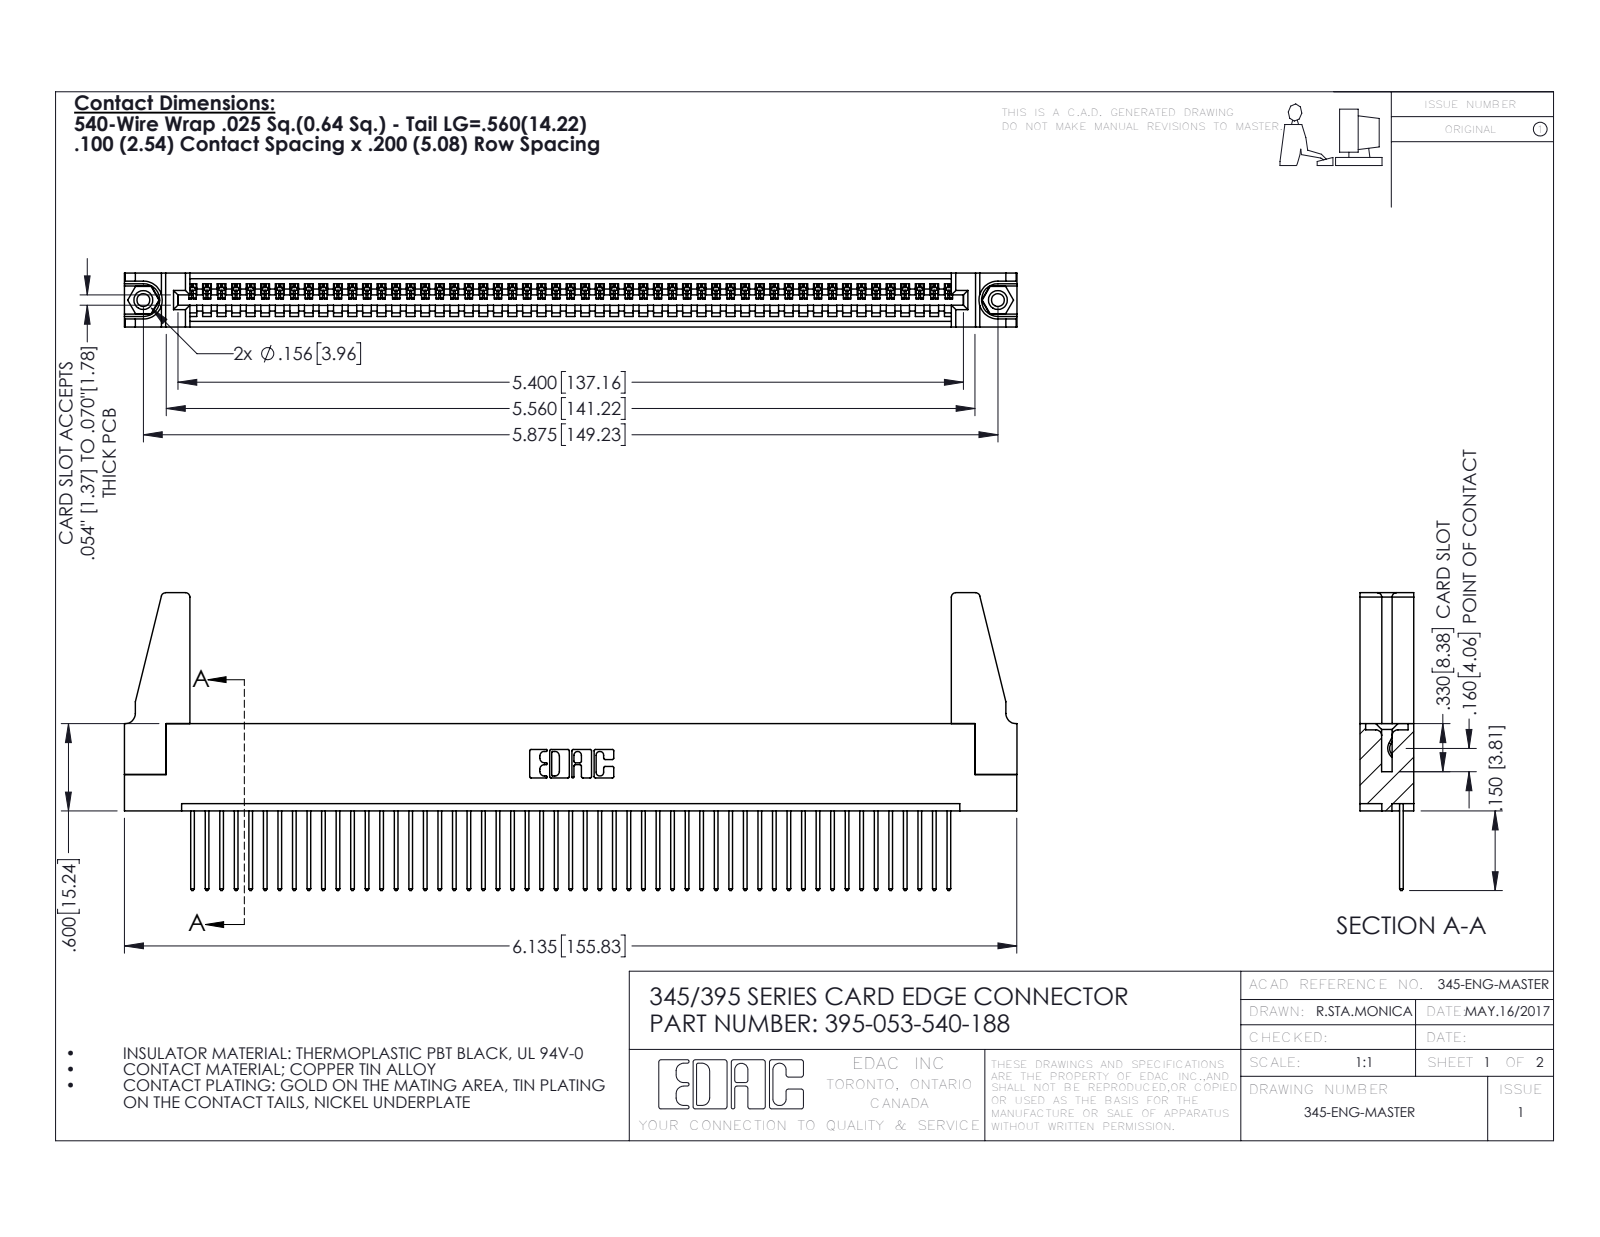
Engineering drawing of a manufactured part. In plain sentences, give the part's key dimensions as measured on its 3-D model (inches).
The part is named "345-220-078_345-220-088; 345 Part_Flush Mounting Lugs - 0.156 Dia-TH; 395-053-540-188; 345-250-001_345-250-001-102 (+1 more)". Its 3-D file was written by "SolidWorks 2016 (CONFIG_CONTROL_DESIGN)". It is 58 solids with 3324 faces: 2272 planar, 1036 cylindrical and 16 other. Overall it measures 6.136 by 2.047 by 0.37 inches. Its volume is 1.112 cubic inches and its surface area 36.71 square inches. Round holes: 2 of diameter 0.089, 2 of diameter 0.125, 2 of diameter 0.156, 1 of diameter 0.064. Round bosses or shafts: 2 of diameter 0.155. Partial cylindrical surfaces (rounded edges, fillets, slot ends): 106 of radius 0.006, 106 of radius 0.01, 22 of radius 0.01, 8 of radius 0.03, 6 of radius 0.007, 6 of radius 0.031, 3 of radius 0.026, 2 of radius 0.031. The main face-to-face distances are 0.072, 0.298, 0.37, 0.098, 0.272, 0.025, 0.2, 0.225, 0.149, 0.072. The hole center spacings are 0.27, 5.639, 5.875.
